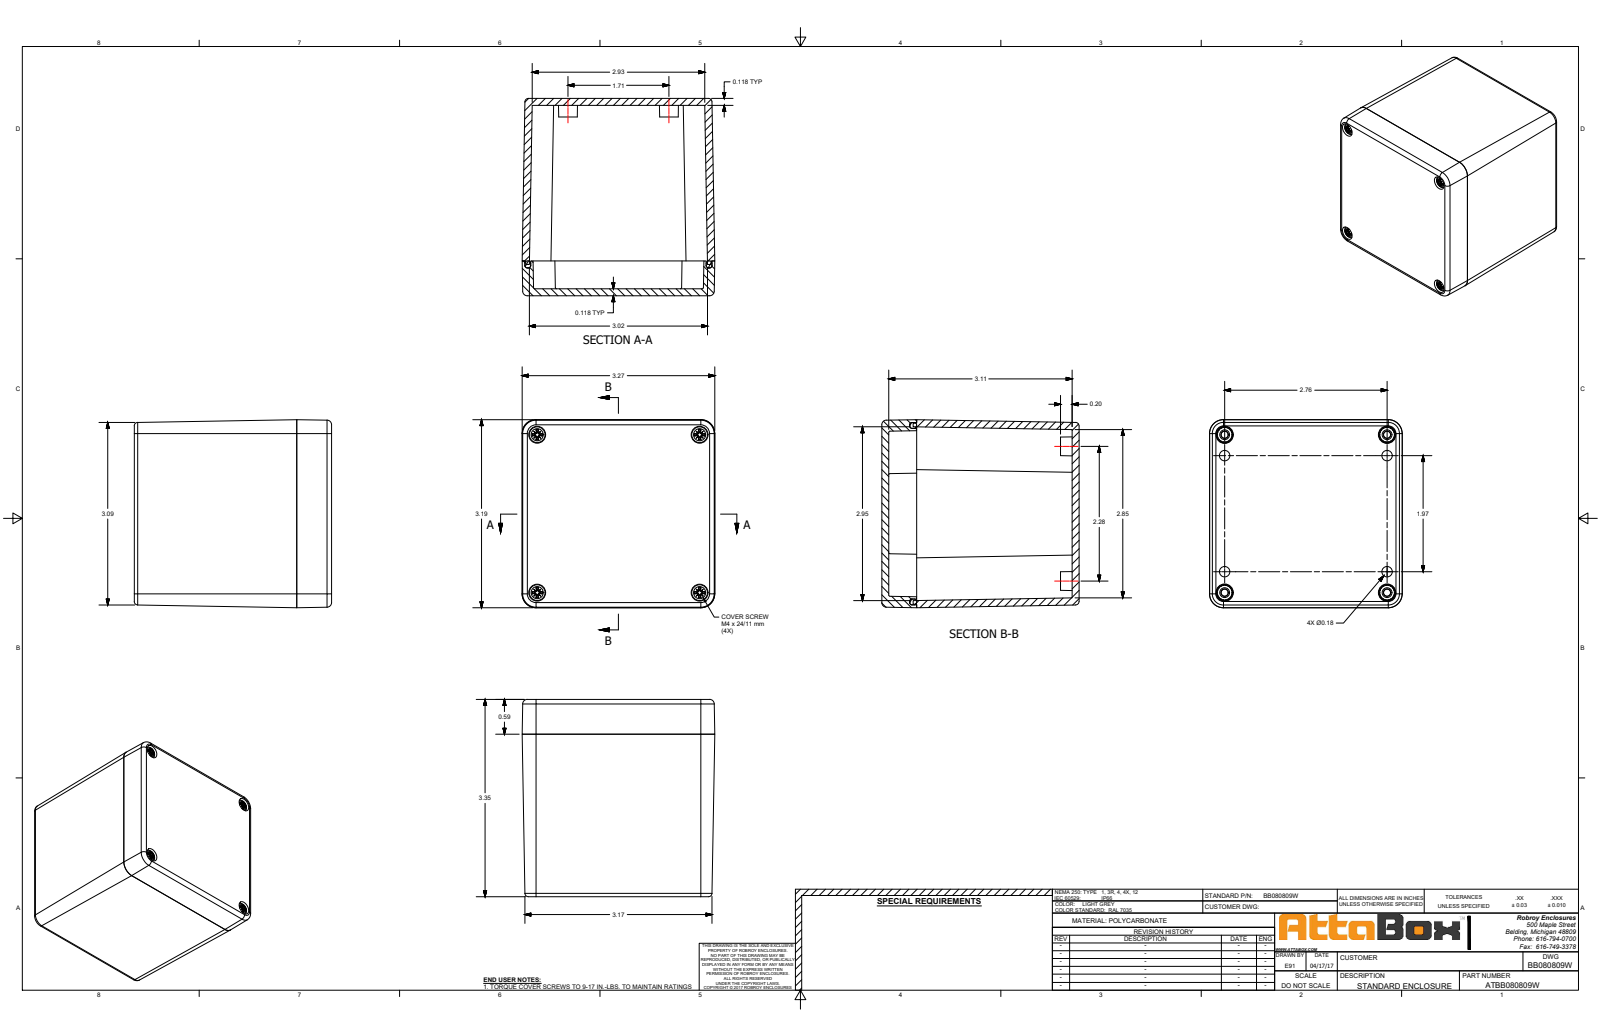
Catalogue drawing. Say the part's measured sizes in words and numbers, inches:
The part is named "BB080809W". Its 3-D file was written by "SolidWorks 2018 (AUTOMOTIVE_DESIGN)". It is 11 solids with 1607 faces: 603 planar, 452 cylindrical and 552 other. Overall it measures 3.346 by 3.268 by 3.189 inches. Its volume is 8.488 cubic inches and its surface area 157.9 square inches. Round holes: 4 of diameter 0.128, 4 of diameter 0.177, 4 of diameter 0.193, 4 of diameter 0.197, 4 of diameter 0.201, 4 of diameter 0.276, 4 of diameter 0.287, 4 of diameter 0.295. Round bosses or shafts: 4 of diameter 0.268, 4 of diameter 0.173, 4 of diameter 0.157, 4 of diameter 0.13. Partial cylindrical surfaces (rounded edges, fillets, slot ends): 32 of radius 0.039, 24 of radius 0.012, 12 of radius 0.197, 8 of radius 0.02, 8 of radius 0.098, 4 of radius 0.059, 4 of radius 0.079, 4 of radius 0.102. The main face-to-face distances are 0.118, 3.228, 0.122, 3.346, 0.124, 3.11, 0.364, 0.488, 2.756, 0.472. The hole center spacings are 0.354, 2.323, 2.756, 2.779, 3.604, 1.969, 2.677, 3.387.
